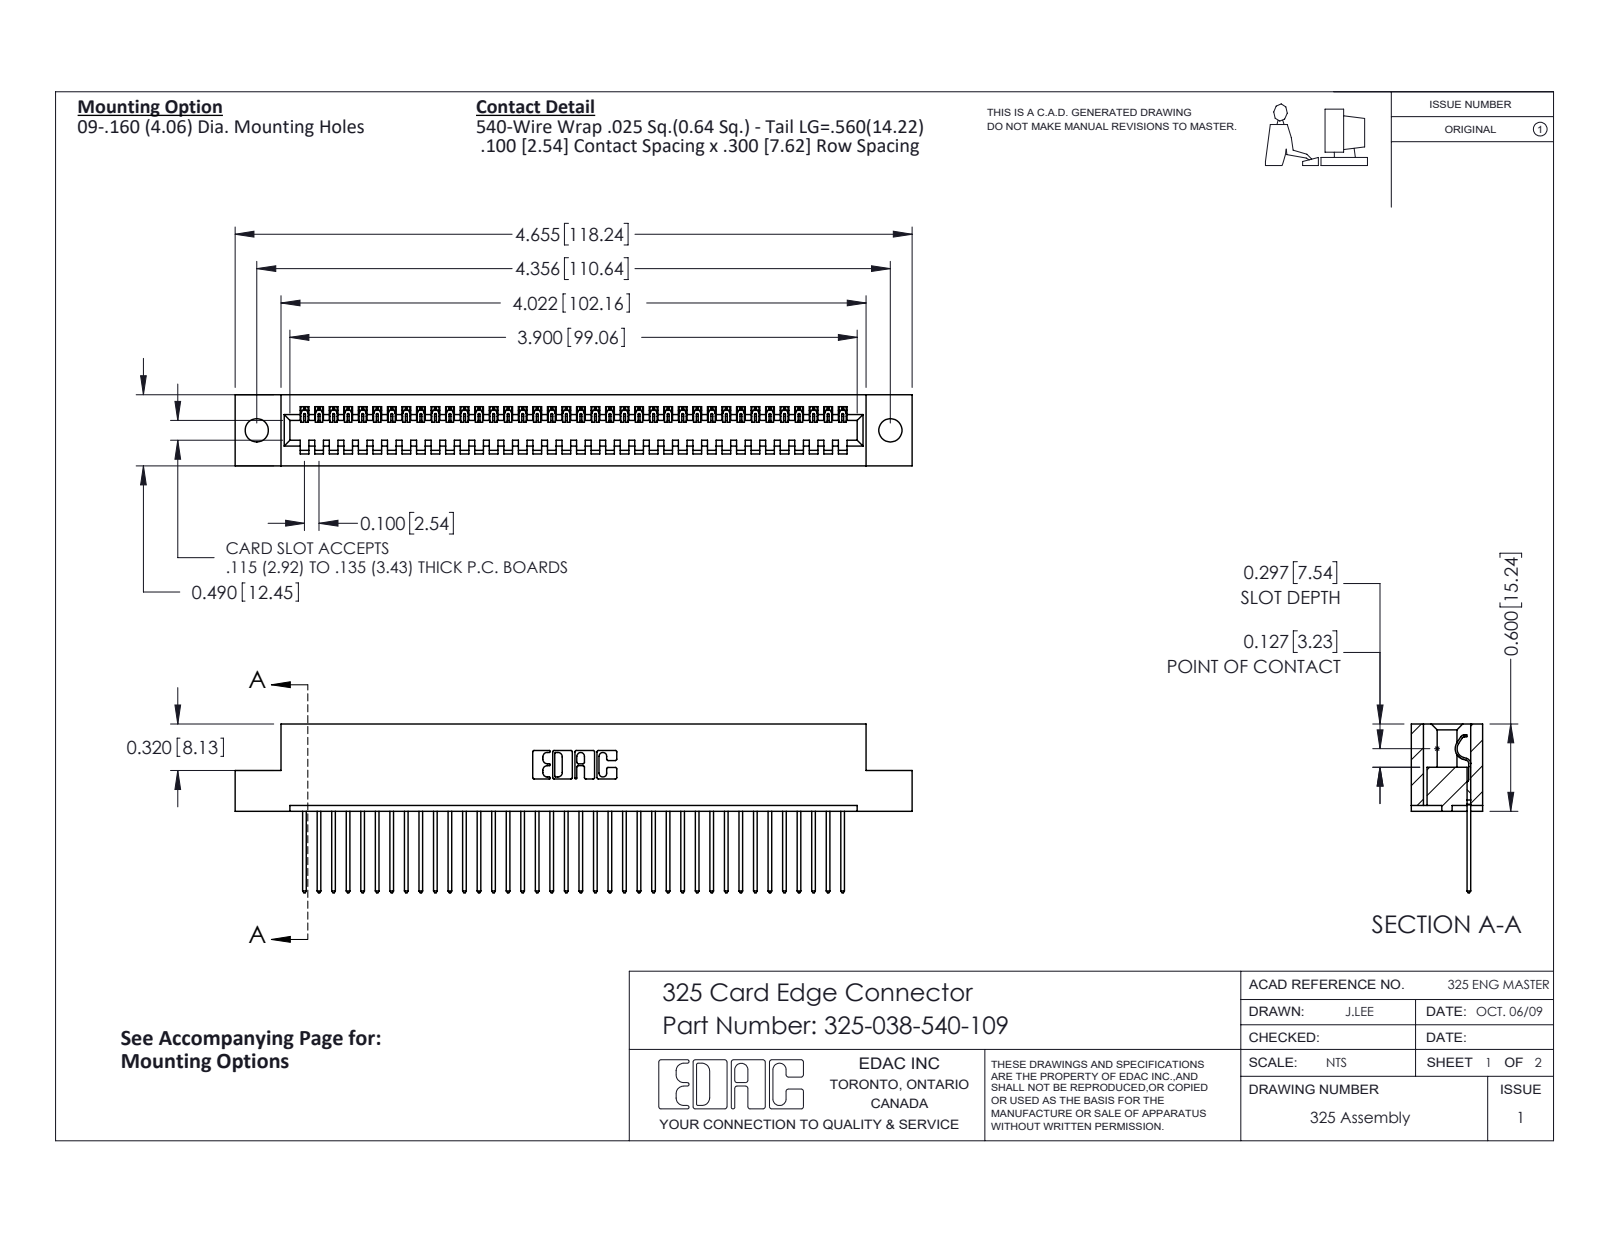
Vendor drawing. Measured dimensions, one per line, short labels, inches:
name: 325-038-540-109; 325 Part_.160 TH; 325-292-001_325-293-140
written by: SolidWorks 2016 (CONFIG_CONTROL_DESIGN)
unit: in
bodies: 39 solids, 2318 faces (1666 planar, 652 cylindrical, 0 other)
size: 4.655 × 1.16 × 0.49
volume: 0.903 in³; area: 25.38 in²
holes: 2× ⌀0.16
rounds: 76× R0.006, 76× R0.01, 22× R0.01, 6× R0.007, 6× R0.031, 3× R0.026, 1× R0.014, 1× R0.022
face distances: 0.083, 0.407, 0.49, 0.3, 0.107, 0.383, 0.025, 0.325, 0.56, 0.263
hole spacings: 4.356
